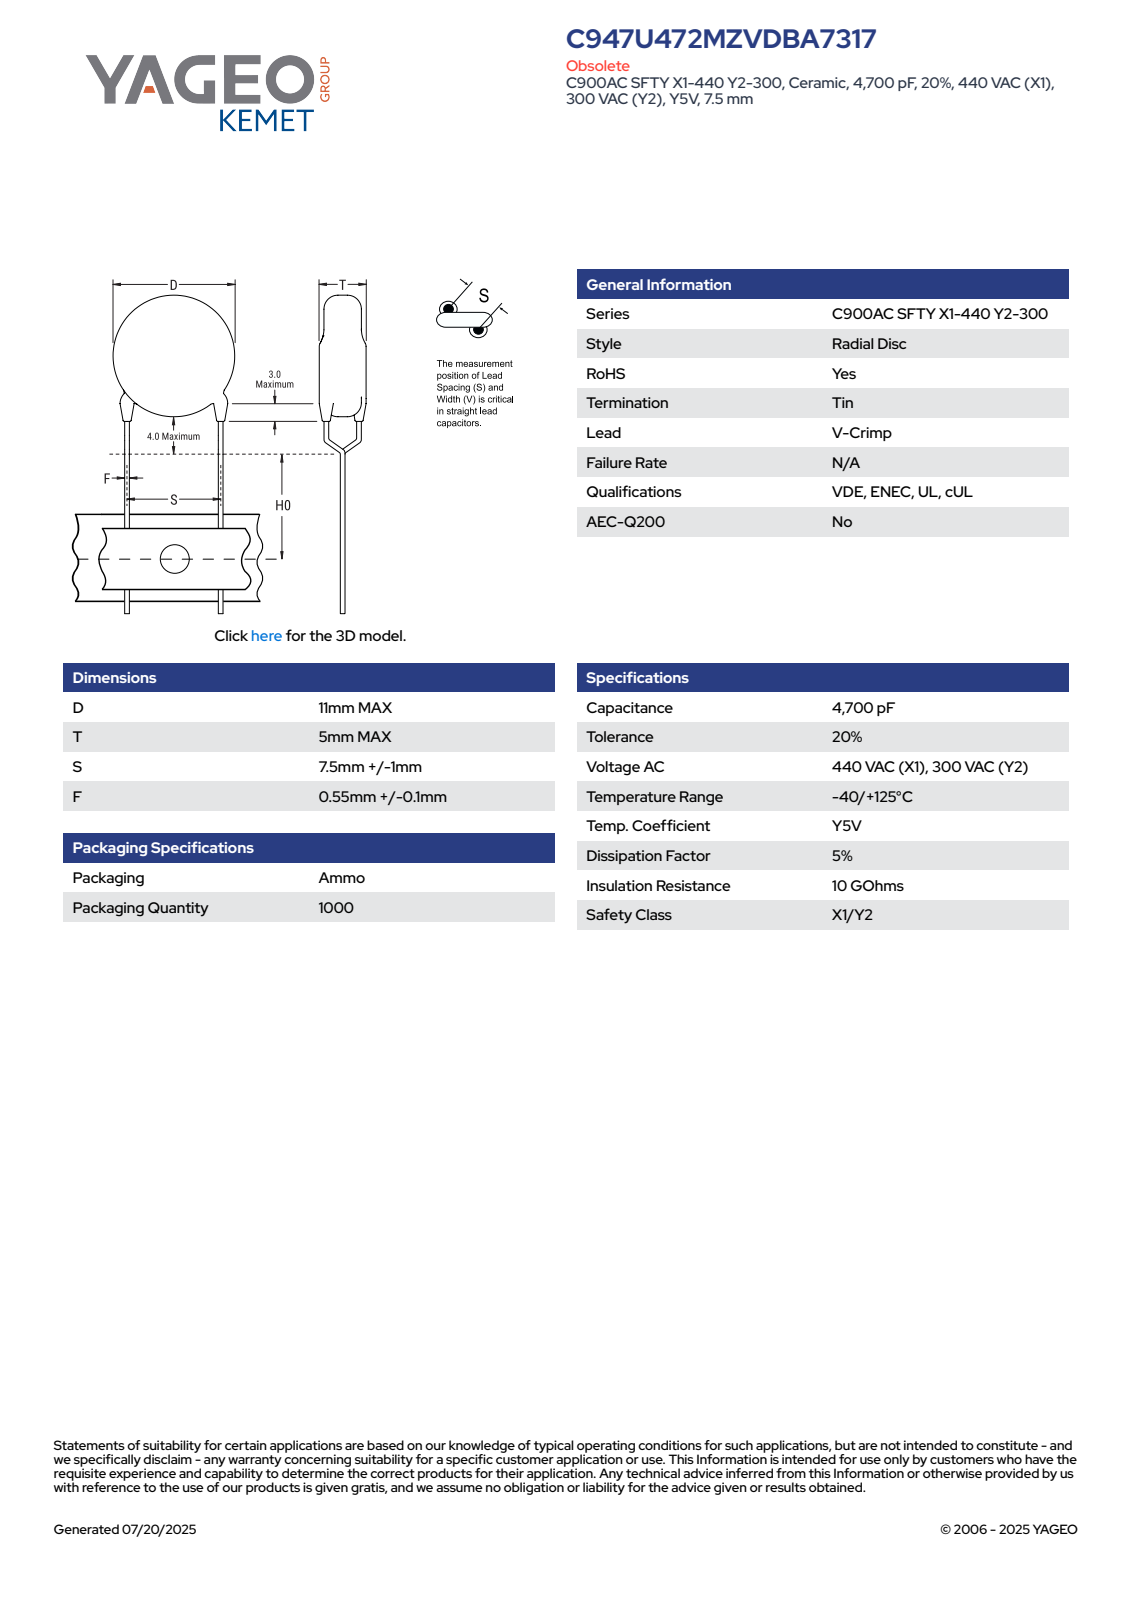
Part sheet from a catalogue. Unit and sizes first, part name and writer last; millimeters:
Units: millimetres
Overall size (bounding box): 34.8 × 11 × 5
Round bosses / shafts (diameter × count): ⌀0.65 ×6, ⌀11 ×1
Main face-to-face distances: 5, 22.9, 30.01, 7.11, 28.58, 5.68, 1.43, 0.39, 0.35, 5.84
Volume: 479 mm³ · Surface area: 451 mm²
Bodies: 5 solids, 93 faces (65 planar, 16 cylindrical, 12 other)
Part name (STEP PRODUCT): CCD_VCC900_D11T5S7.5LL20F0.65
STEP written by: SolidWorks 2014 (AUTOMOTIVE_DESIGN)
